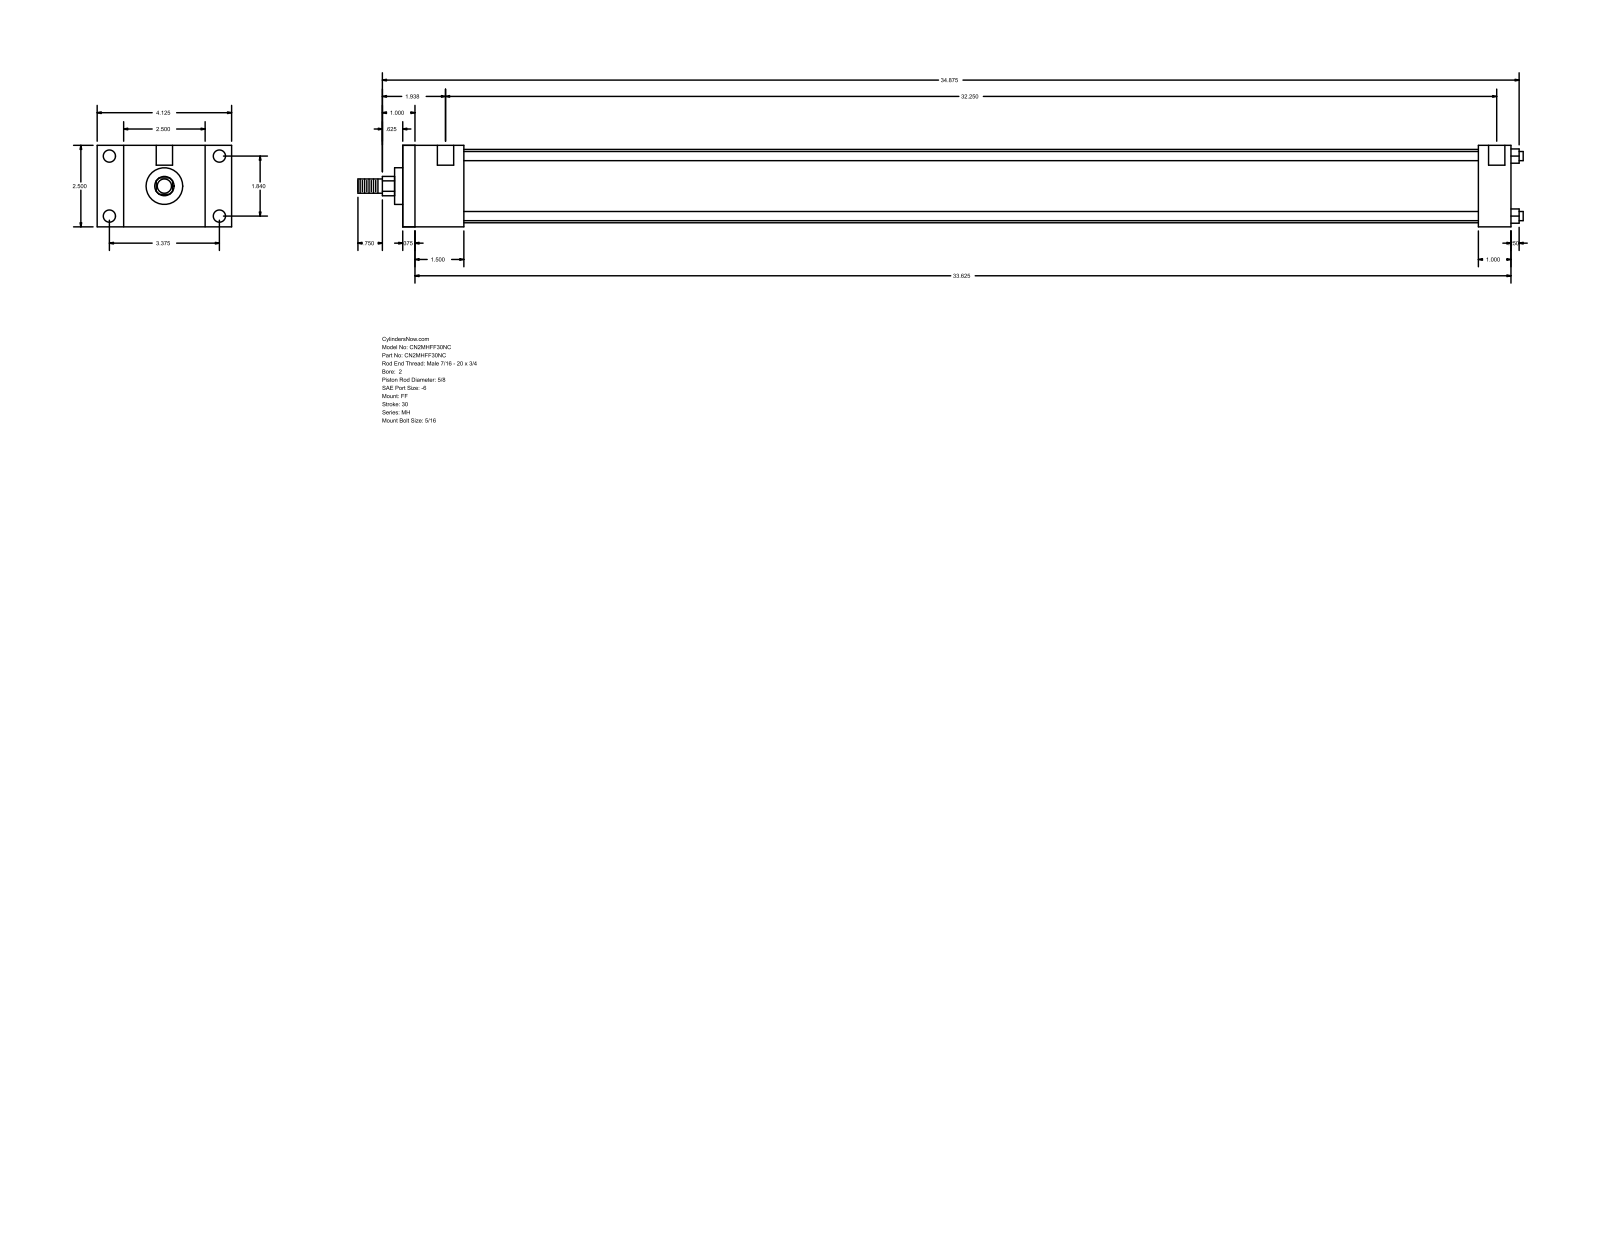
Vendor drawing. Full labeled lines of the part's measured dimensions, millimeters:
Part name (STEP PRODUCT): MH_FF__0200_0.625
STEP written by: GSSL Pune (CONFIG_CONTROL_DESIGN)
Units: millimetres
Bodies: 0 solids, 92 faces (64 planar, 28 cylindrical, 0 other)
Overall size (bounding box): 908.05 × 104.78 × 63.5
Round holes (diameter × count): ⌀5.56 ×4, ⌀9.53 ×4, ⌀12.7 ×2
Round bosses / shafts (diameter × count): ⌀7.14 ×4, ⌀57.15 ×1, ⌀28.57 ×1, ⌀15.88 ×1, ⌀11.11 ×1
Partial cylindrical surfaces — rounded edges, fillets, slot ends (radius × count): R7.54 ×1
Main face-to-face distances: 63.5, 863.6, 9.52, 854.08, 25.4, 38.1, 47.62, 838.2, 828.68, 790.58
Hole centre spacings: 46.74, 85.72, 97.63, 827.09, 3.18, 4.76, 819.15, 822.33
